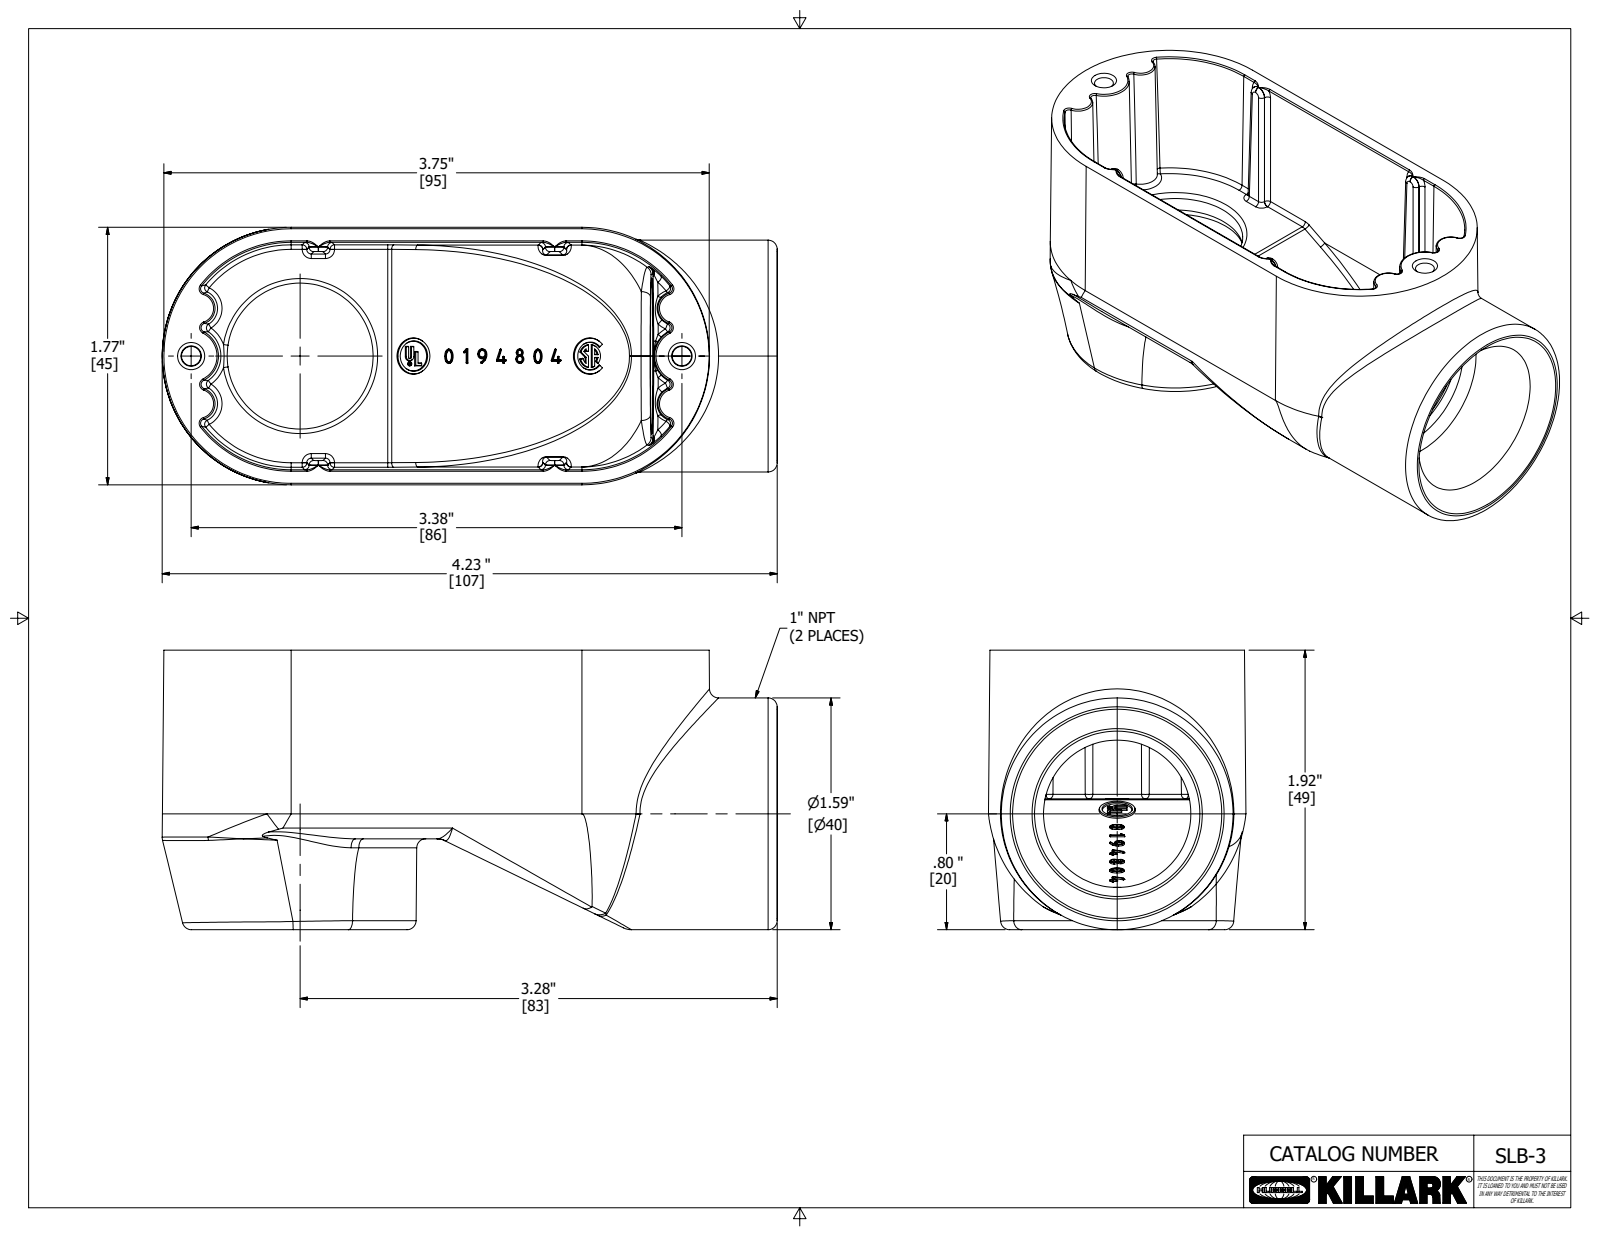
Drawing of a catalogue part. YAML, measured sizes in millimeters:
part_name: "0194804 -2"
step_written_by: "Autodesk Inventor 2020 (AUTOMOTIVE_DESIGN)"
units: millimeters
bodies: {solids: 1, faces: 484, planar: 120, cylindrical: 64, other: 300}
overall_size: [107.4, 48.8, 45]
volume: 58240
surface_area: 29170
round_holes:
  - {diameter: 25.7, count: 1}
round_bosses_or_shafts:
  - {diameter: 40.5, count: 1}
partial_cylinders:
  - {radius: 0.8, count: 29}
  - {radius: 1.6, count: 6}
  - {radius: 0.3, count: 2}
  - {radius: 2.4, count: 2}
  - {radius: 19.3, count: 2}
  - {radius: 22.5, count: 2}
  - {radius: 3.2, count: 1}
face_to_face_distances: [2.3, 26, 1.6, 7, 32.9, 15.9, 22.9, 48.8, 39.3, 23.4]
